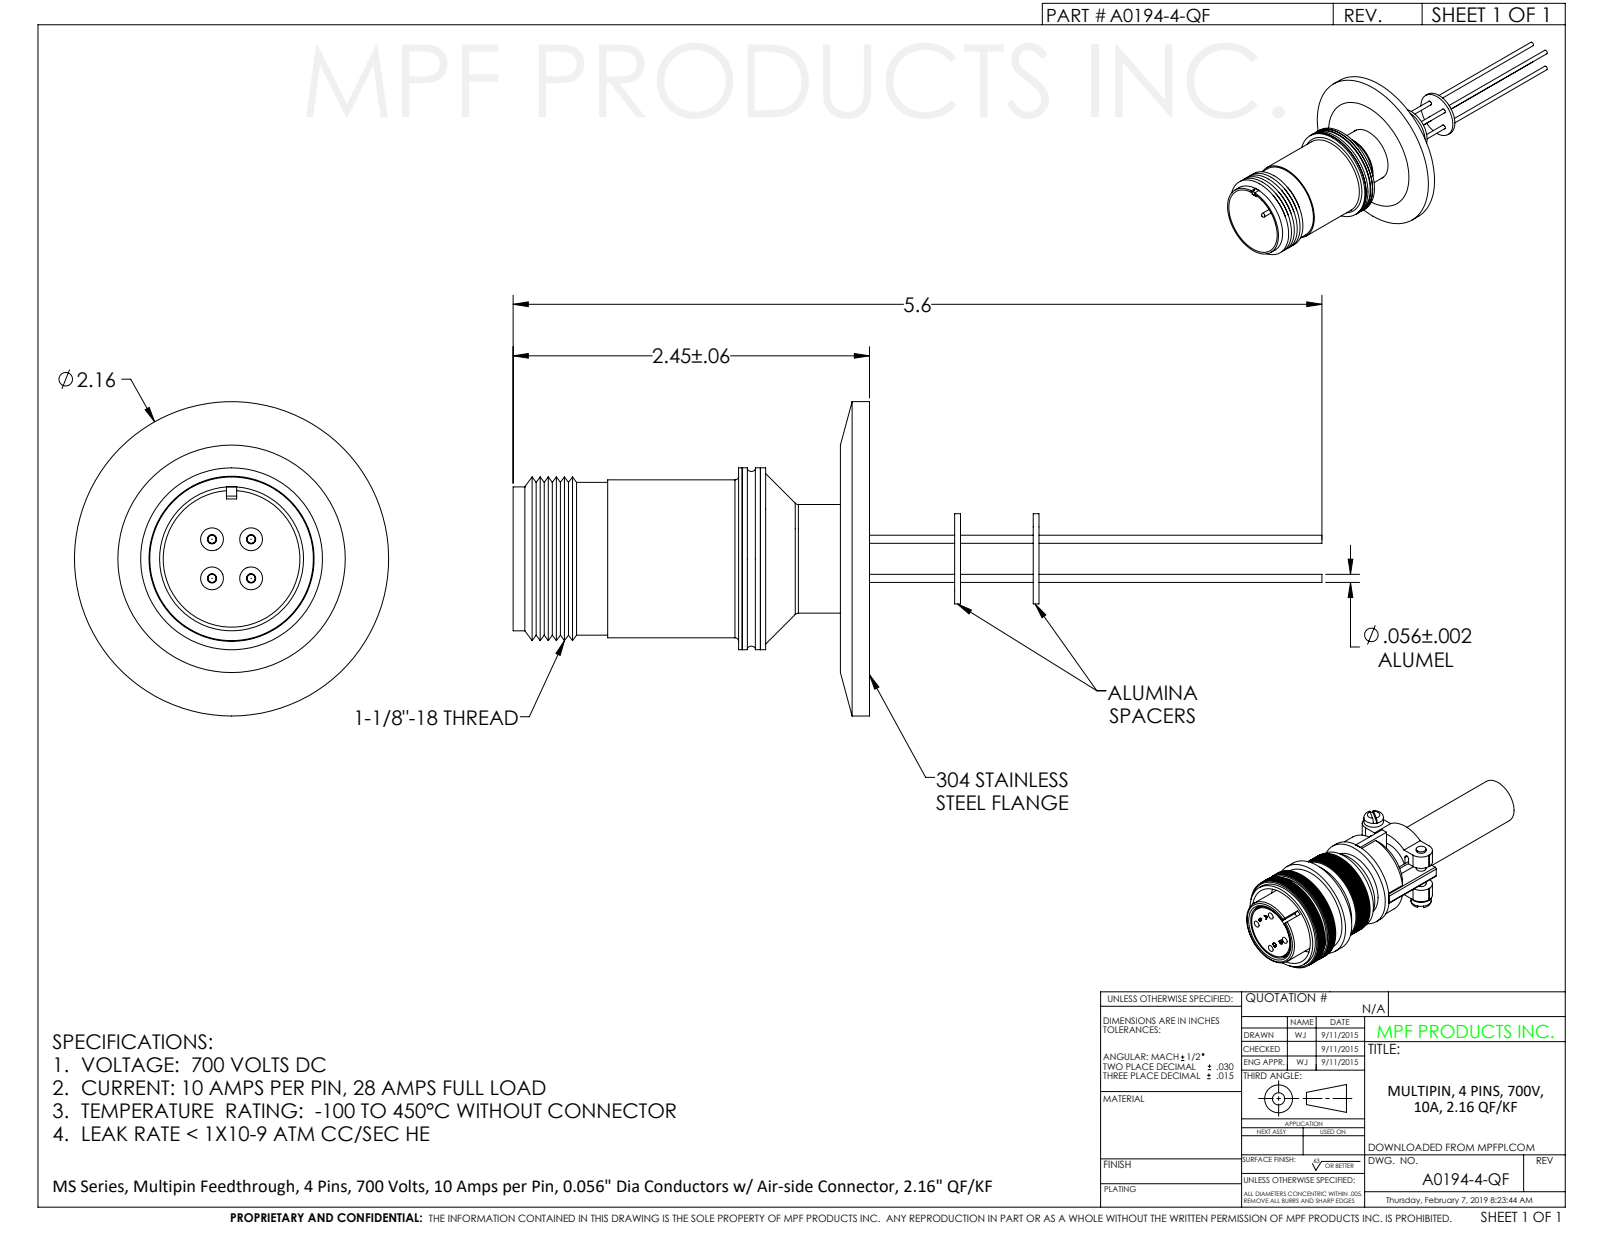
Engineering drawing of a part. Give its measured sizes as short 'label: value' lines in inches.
name: A0194-4-QF
written by: SolidWorks 2012 (CONFIG_CONTROL_DESIGN)
unit: in
bodies: 1 solid, 197 faces (53 planar, 94 cylindrical, 50 other)
size: 5.595 × 2.165 × 2.165
volume: 1.122 in³; area: 35.88 in²
holes: 1× ⌀0.675, 1× ⌀0.75, 1× ⌀0.94, 1× ⌀0.96, 1× ⌀0.97, 1× ⌀1.035, 1× ⌀1.63
bosses: 4× ⌀0.187, 4× ⌀0.167, 4× ⌀0.056, 1× ⌀2.165, 1× ⌀1.38, 1× ⌀1.25, 1× ⌀1.085, 1× ⌀1.05
face distances: 0.2, 1.305, 1.105, 0.04, 1.255, 1.055, 0.05, 0.105, 0.095, 1.15
